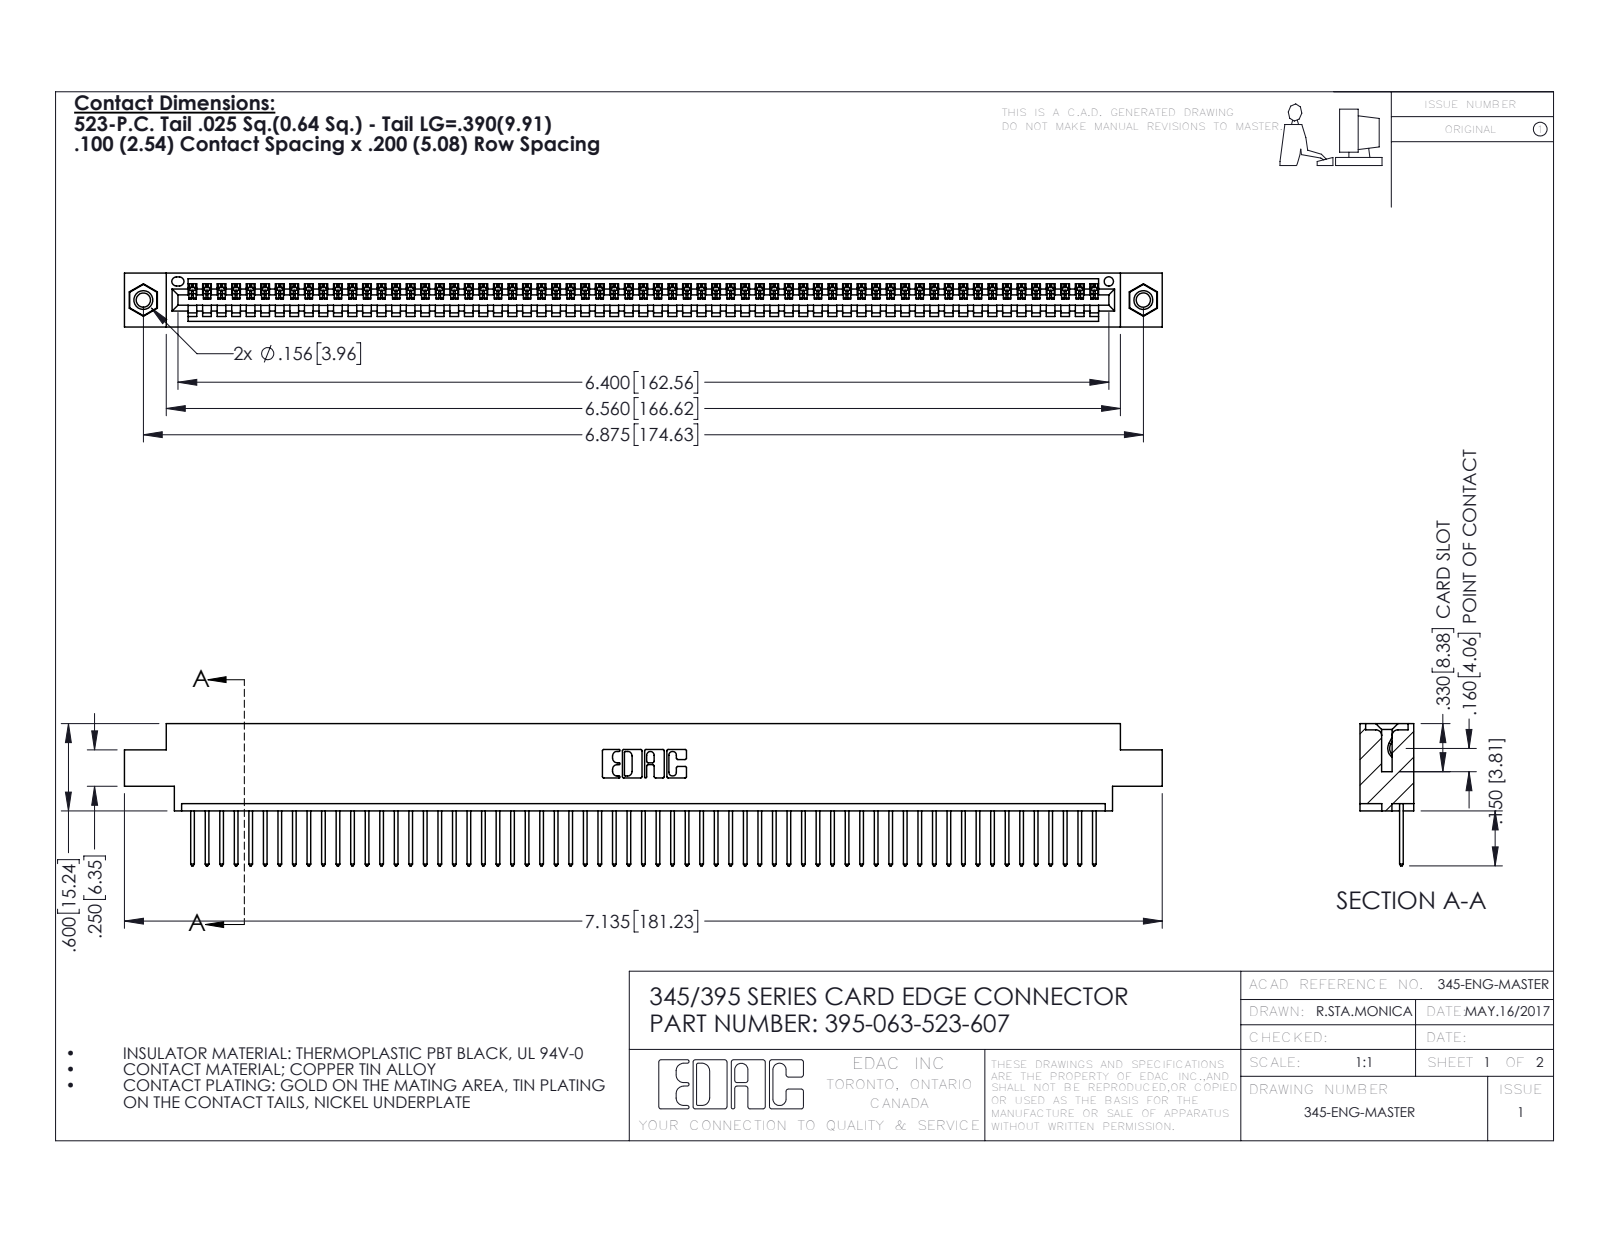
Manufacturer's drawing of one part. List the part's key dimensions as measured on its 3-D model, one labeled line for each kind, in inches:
Part name (STEP PRODUCT): 395-063-523-607; 345-292-001_345-293-123; 345 Part_0.170 Offset - 0.156 Dia-TI; 345-250-001_345-250-005-103
STEP written by: SolidWorks 2016 (CONFIG_CONTROL_DESIGN)
Units: inches
Bodies: 66 solids, 3844 faces (2636 planar, 1192 cylindrical, 16 other)
Overall size (bounding box): 7.135 × 0.977 × 0.37
Volume: 1.052 in³ · Surface area: 36.29 in²
Round holes (diameter × count): ⌀0.098 ×2, ⌀0.125 ×2, ⌀0.156 ×2, ⌀0.064 ×1
Round bosses / shafts (diameter × count): ⌀0.155 ×2
Partial cylindrical surfaces — rounded edges, fillets, slot ends (radius × count): R0.006 ×126, R0.01 ×126, R0.01 ×22, R0.007 ×6, R0.031 ×6, R0.026 ×3, R0.031 ×2, R0.04 ×2
Main face-to-face distances: 0.072, 0.298, 0.37, 0.2, 0.098, 0.272, 0.025, 0.225, 0.175, 0.149
Hole centre spacings: 0.27, 6.639, 6.875
